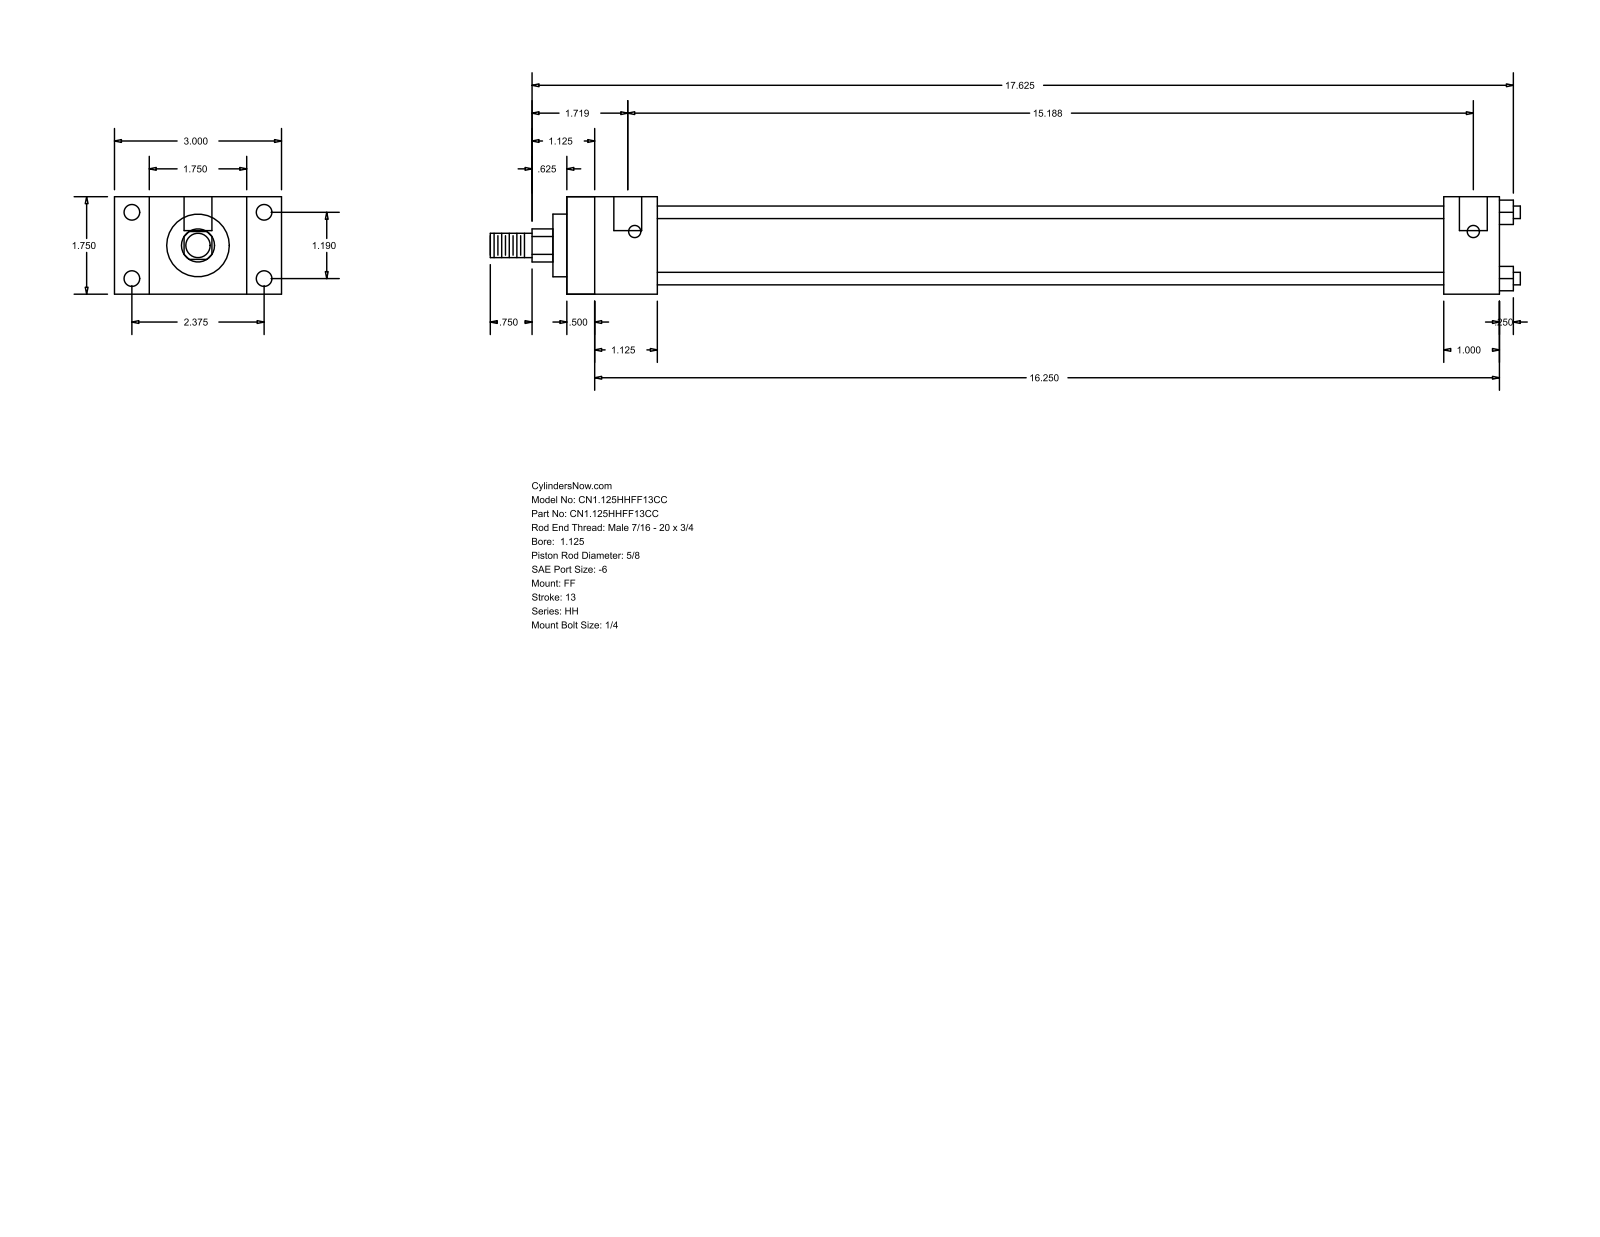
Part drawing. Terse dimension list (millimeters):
name: HH_FF__0112_0.625
written by: GSSL Pune (CONFIG_CONTROL_DESIGN)
unit: mm
bodies: 0 solids, 92 faces (64 planar, 28 cylindrical, 0 other)
size: 469.9 × 76.2 × 44.45
holes: 4× ⌀5.56, 4× ⌀7.14, 2× ⌀12.7
bosses: 4× ⌀5.71, 1× ⌀34.92, 1× ⌀28.57, 1× ⌀15.88, 1× ⌀11.11
rounds: 1× R7.54
face distances: 44.46, 425.44, 12.69, 412.75, 15.87, 28.58, 60.33, 41.27, 400.05, 387.36
hole spacings: 30.22, 60.32, 67.47, 382.59, 3.17, 385.76
